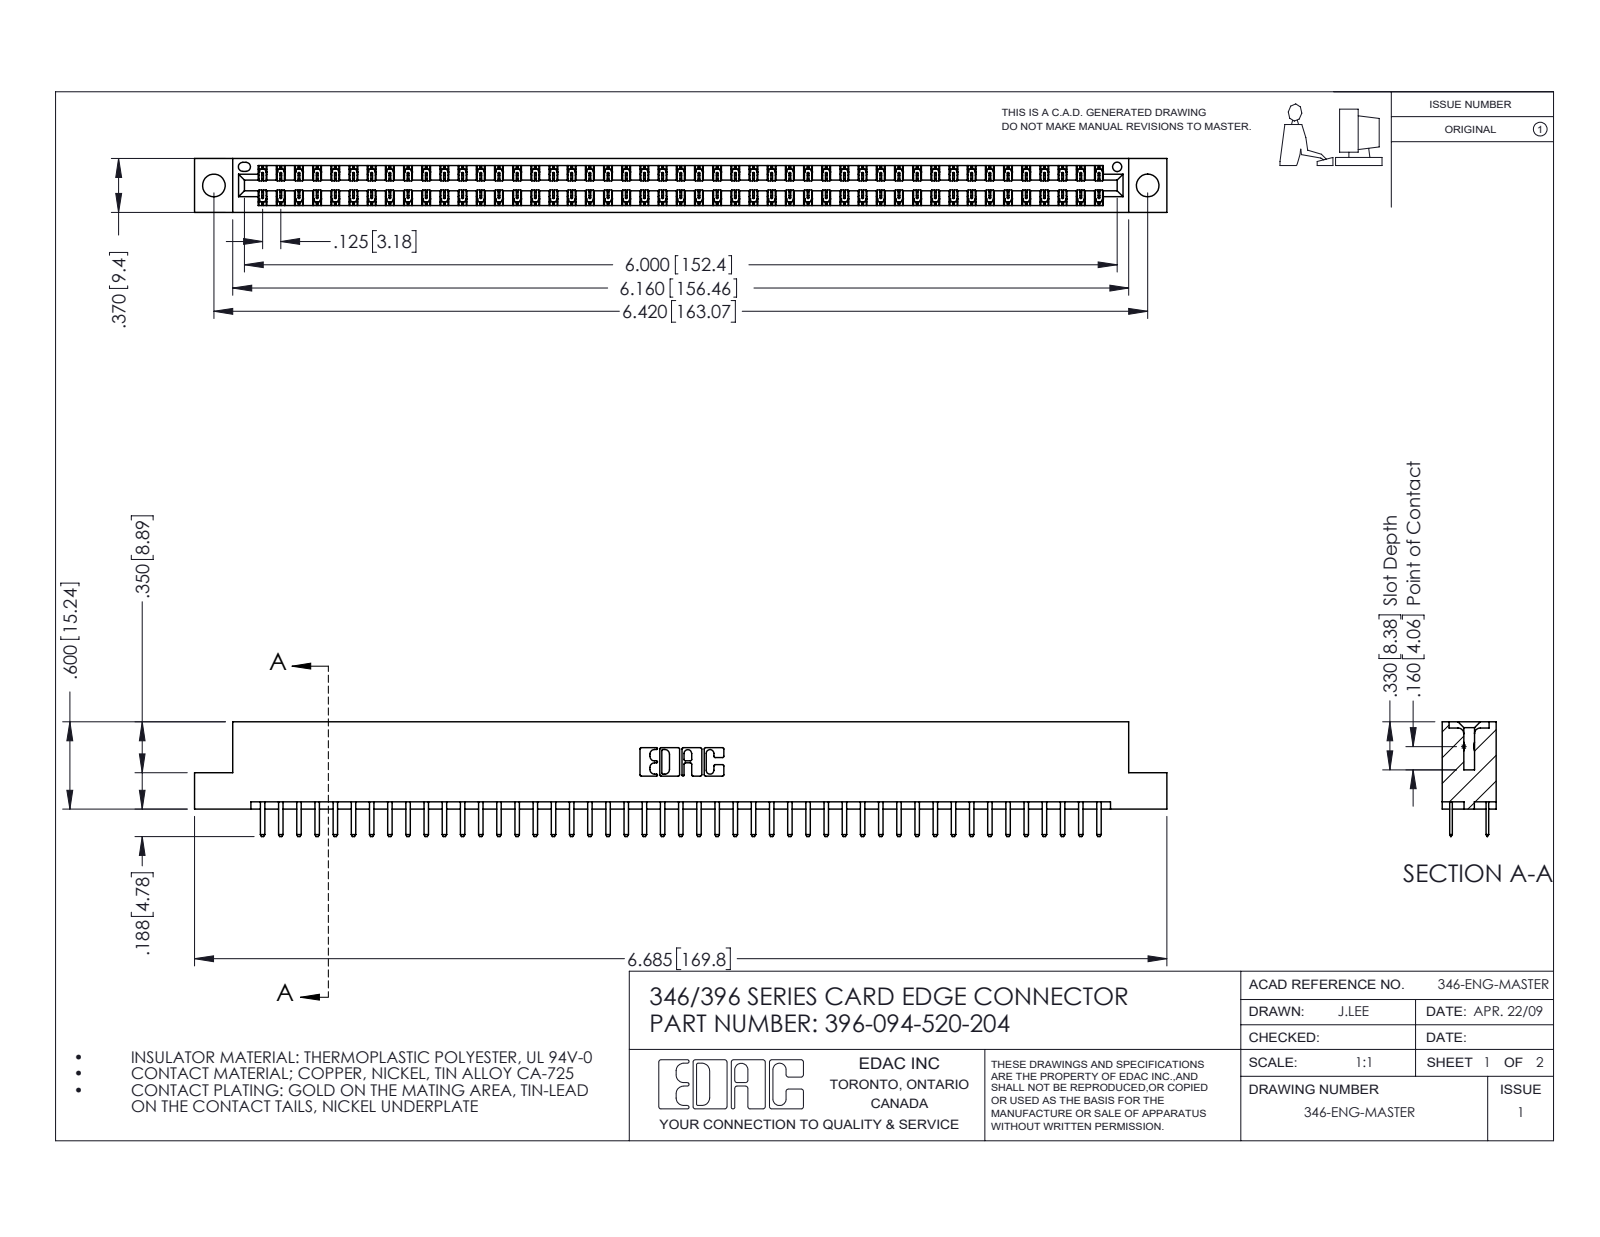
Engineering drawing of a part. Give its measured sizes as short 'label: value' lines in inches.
name: 345-292-001_345-293-120; 346 Part_Flush Mounting Lugs - 0.156 Dia-TH; 396-094-520-204
written by: SolidWorks 2016 (CONFIG_CONTROL_DESIGN)
unit: in
bodies: 95 solids, 5386 faces (3554 planar, 1832 cylindrical, 0 other)
size: 6.685 × 0.788 × 0.37
volume: 1.005 in³; area: 34.77 in²
holes: 2× ⌀0.156, 1× ⌀0.064
rounds: 141× R0.006, 98× R0.01, 22× R0.01, 6× R0.007, 6× R0.031, 3× R0.026, 2× R0.014, 2× R0.022
face distances: 0.048, 0.322, 0.25, 0.37, 0.275, 0.072, 0.298, 0.025, 0.148, 0.222
hole spacings: 0.246, 6.211, 6.42
